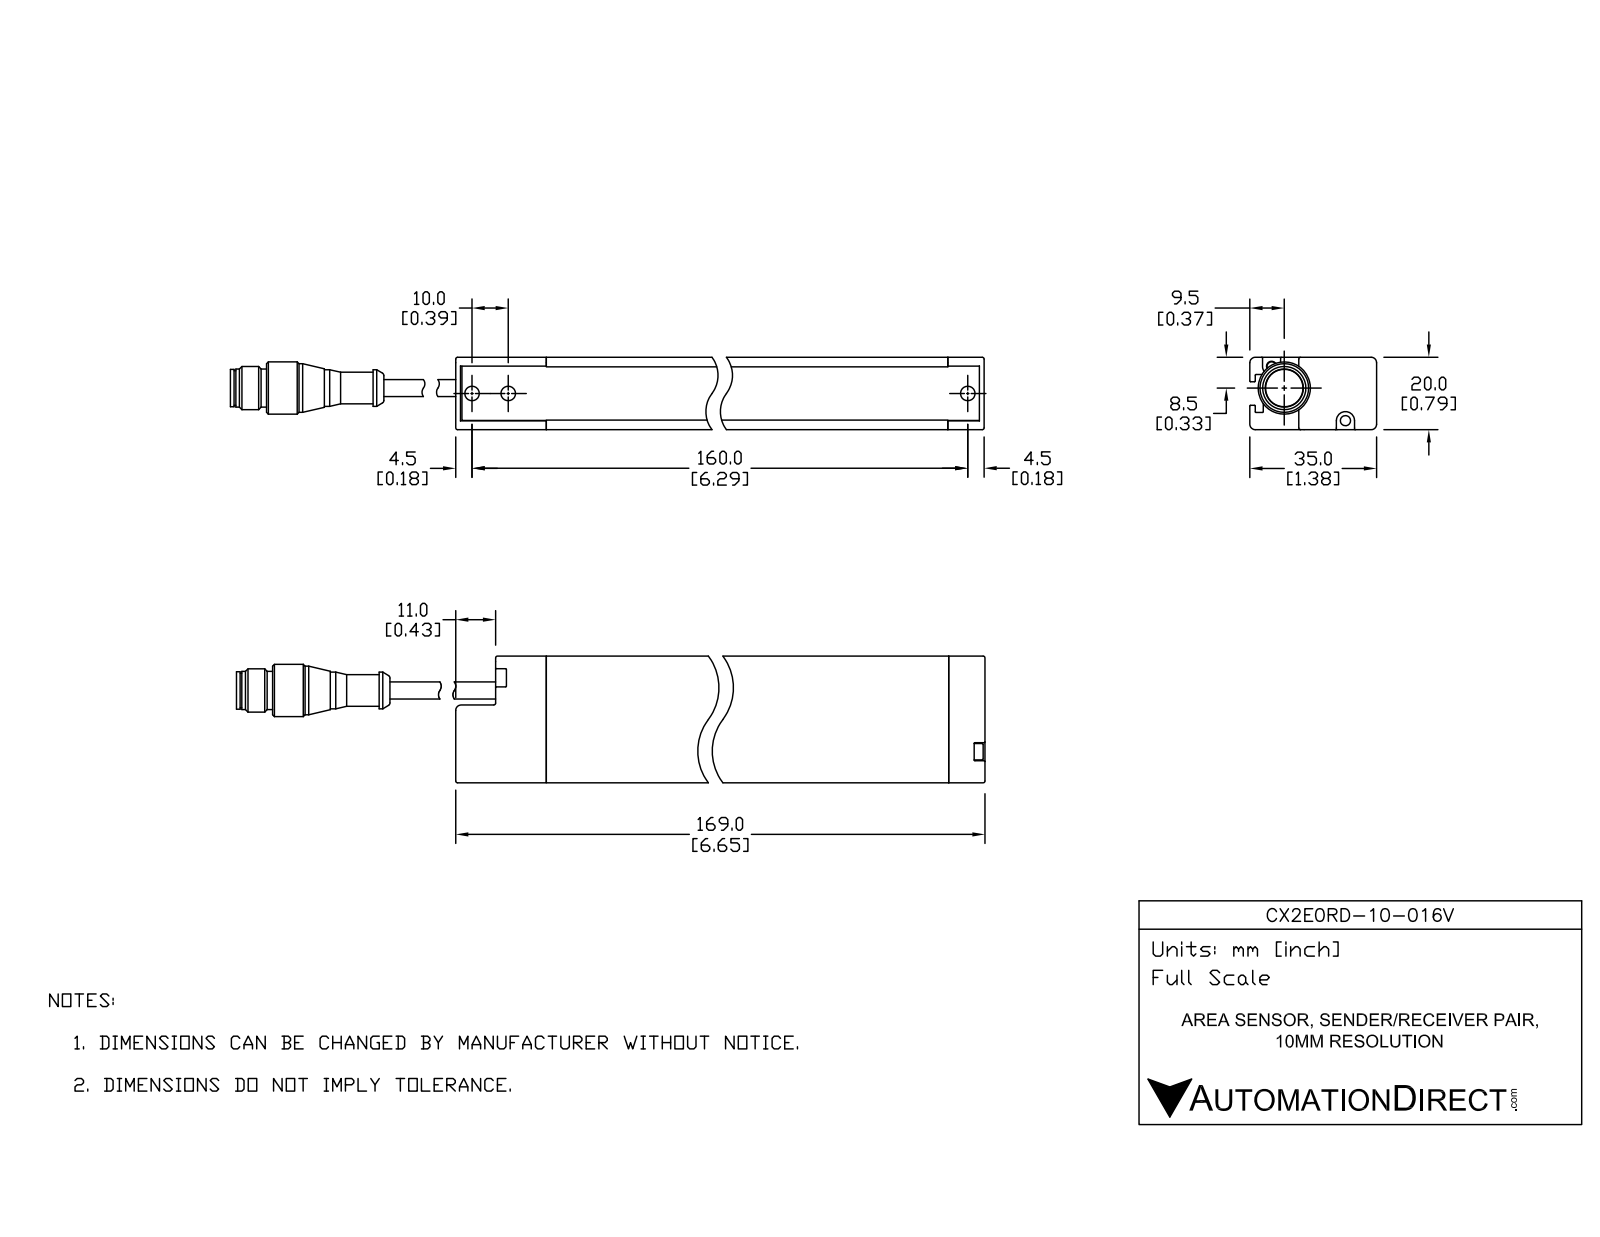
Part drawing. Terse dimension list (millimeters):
name: oa0
written by: Unknown (AUTOMOTIVE_DESIGN)
unit: mm
bodies: 16 solids, 688 faces (226 planar, 266 cylindrical, 196 other)
size: 548.58 × 248.34 × 149.87
volume: 236 929 mm³; area: 66 171 mm²
holes: 8× ⌀2.8, 2× ⌀6.5, 2× ⌀8
bosses: 8× ⌀2.01, 4× ⌀4.5, 4× ⌀2.5, 2× ⌀14.42, 2× ⌀13.42, 2× ⌀11.93, 2× ⌀10.53, 2× ⌀10.33
rounds: 96× R0.2, 26× R0.5, 10× R1.5, 8× R2.5, 4× R0.3
face distances: 129.87, 20, 2, 149.87, 109.87, 481.29, 14.73, 30.9, 510.29, 3.7
hole spacings: 15, 20.4, 25.32, 532.28, 6.95, 9.66, 17.93, 19.15
